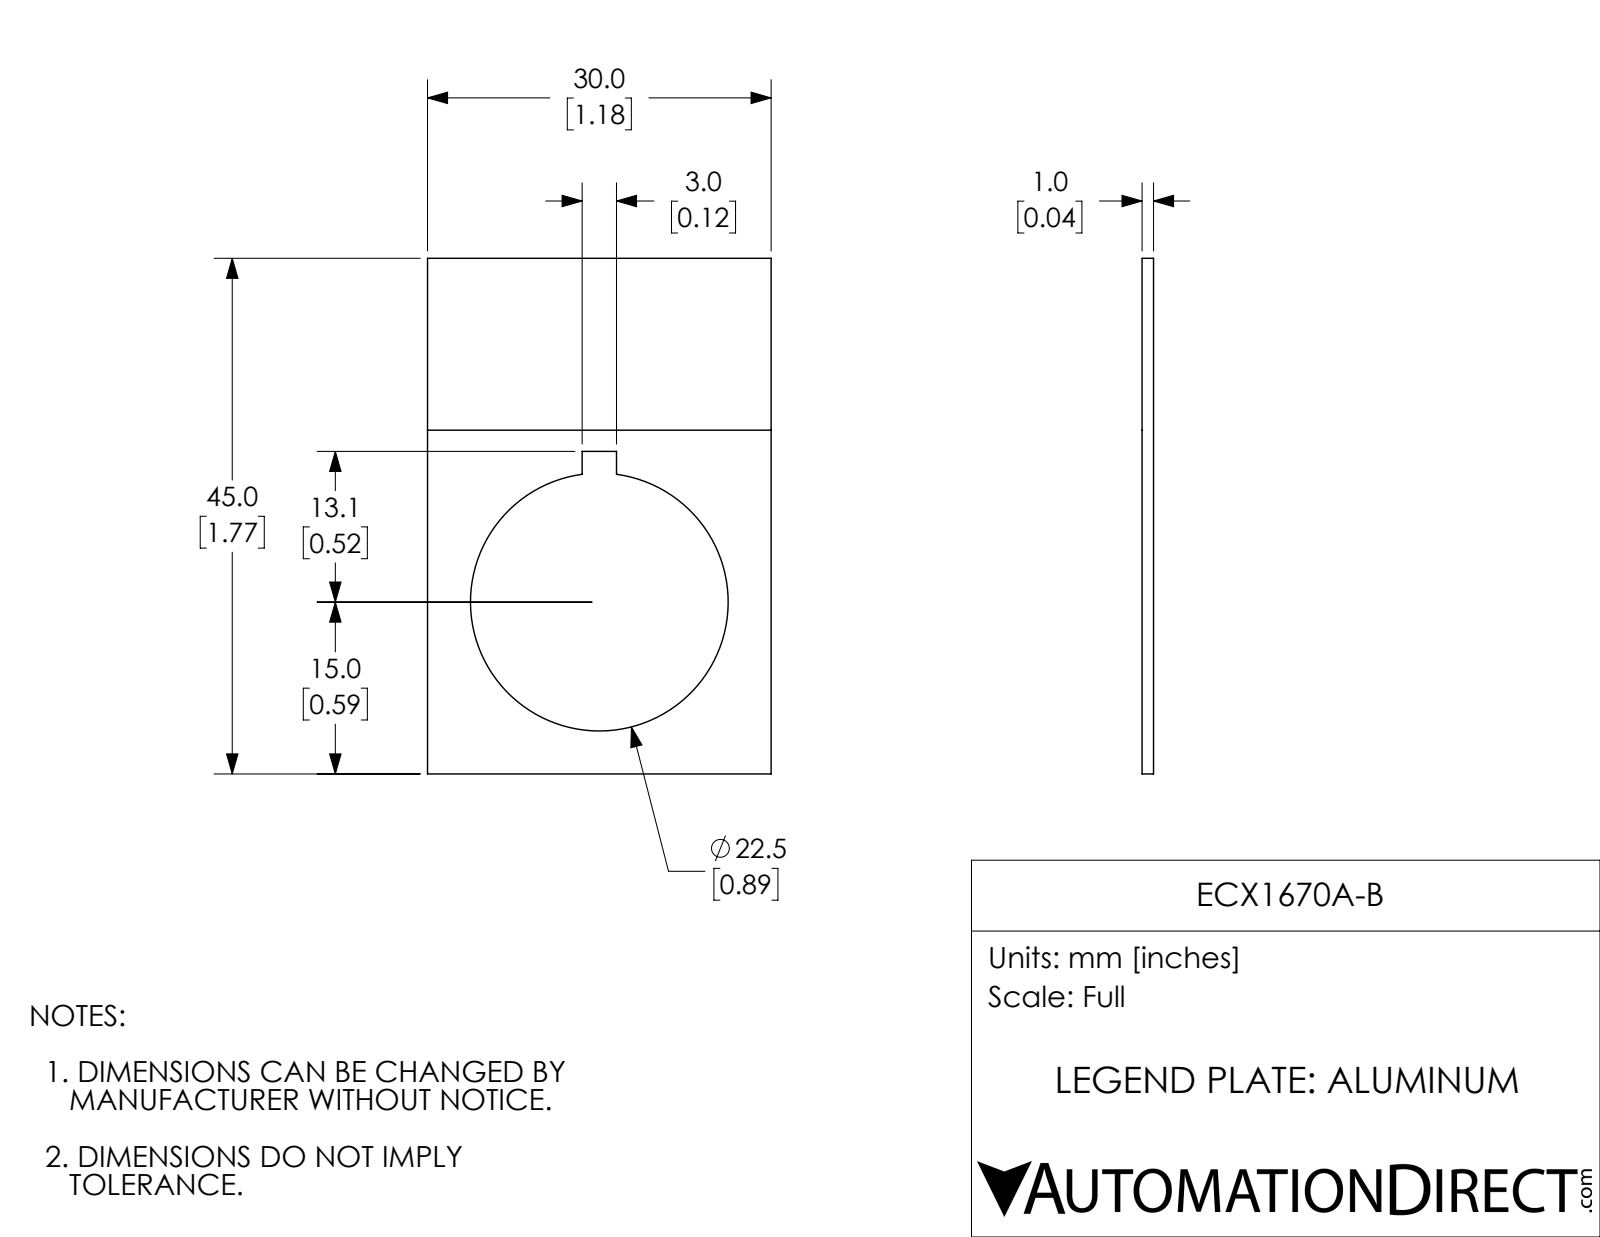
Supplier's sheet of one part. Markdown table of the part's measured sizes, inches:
| quantity | value |
| --- | --- |
| part name | ECX1670A-B |
| STEP written by | SolidWorks 2017 (AUTOMOTIVE_DESIGN) |
| units | inches |
| bodies | 1 solid, 13 faces (10 planar, 3 cylindrical, 0 other) |
| overall size | 1.772 × 1.181 × 0.039 |
| volume | 0.058 in³ |
| surface area | 3.283 in² |
| round holes (diameter × count) | 0.886 × 1 |
| main face-to-face distances | 0.039, 1.181, 1.772, 0.531, 0.65, 1.108, 0.663, 0.118 |
